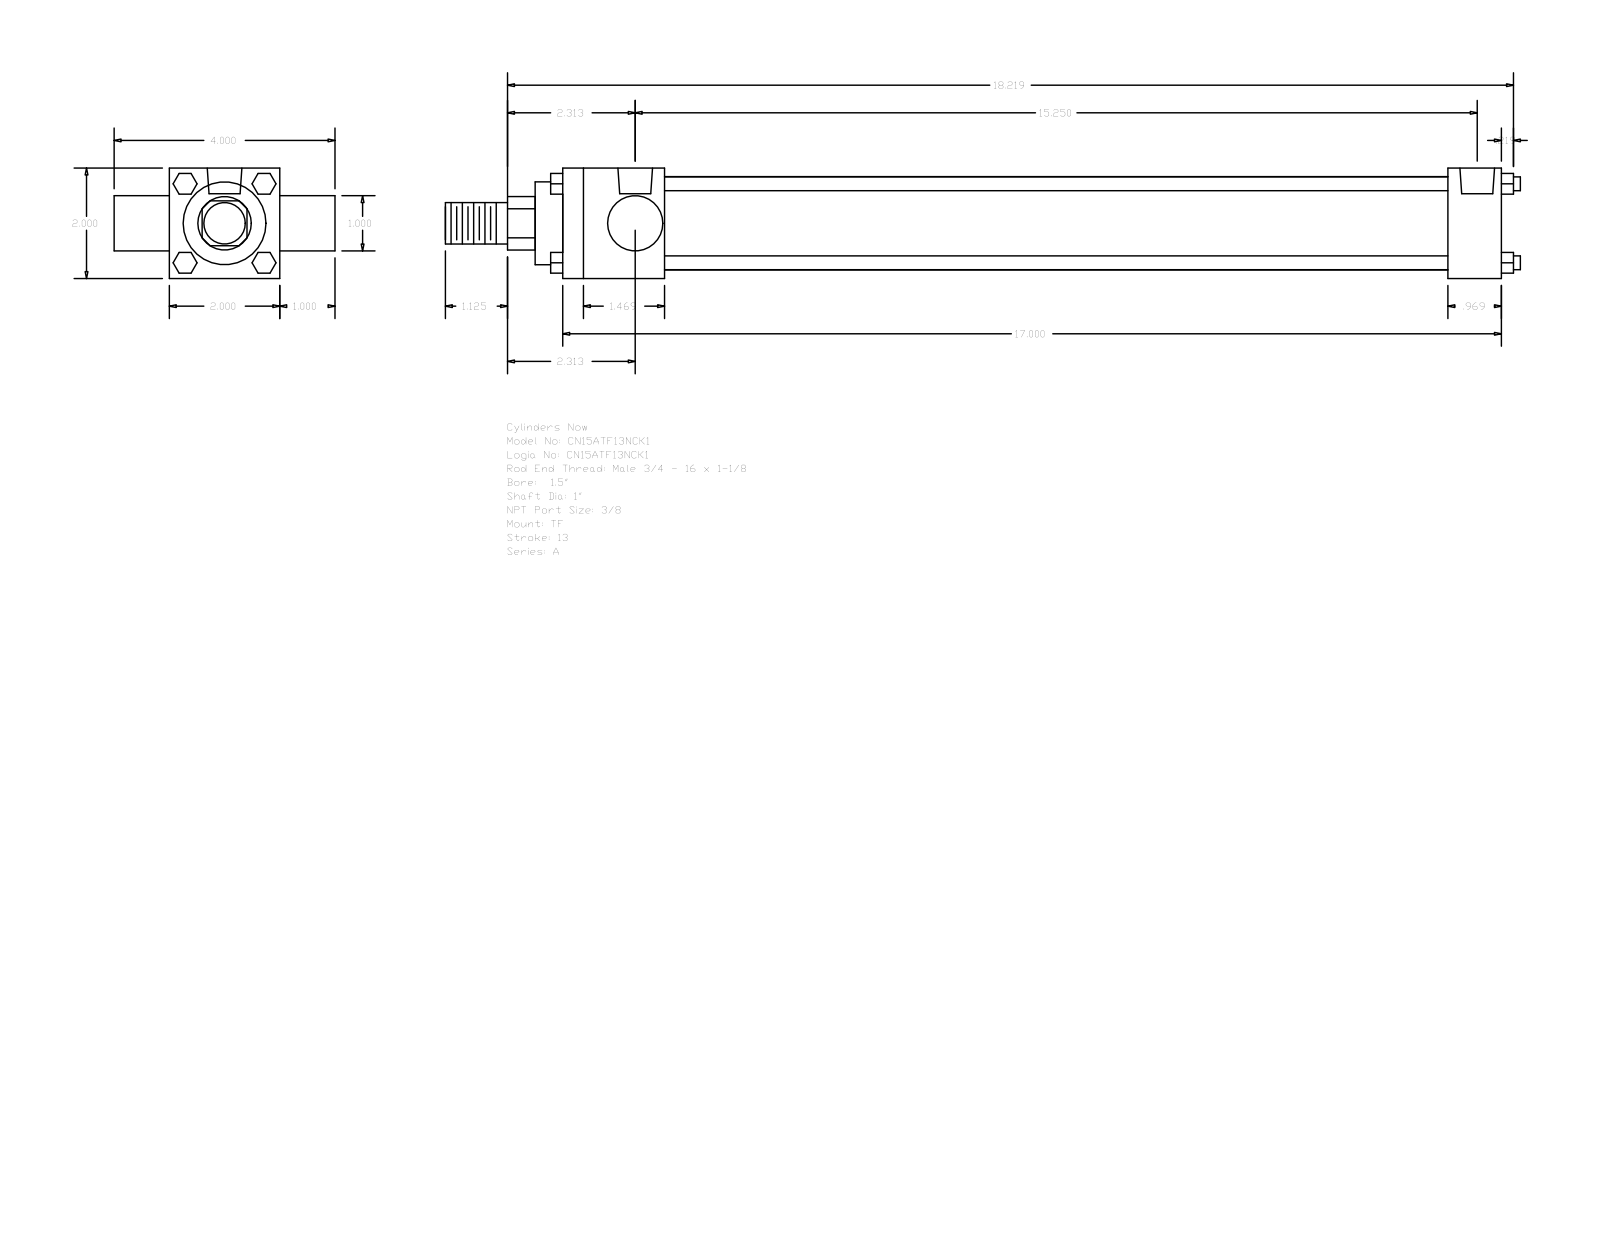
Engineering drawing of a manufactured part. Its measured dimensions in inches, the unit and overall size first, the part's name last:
Units: inches
Overall size (bounding box): 19.469 × 4 × 2
Round holes (diameter × count): ⌀0.219 ×3, ⌀0.627 ×2
Round bosses / shafts (diameter × count): ⌀0.25 ×4, ⌀1 ×2, ⌀1.69 ×1, ⌀1.5 ×1, ⌀0.75 ×1
Partial cylindrical surfaces — rounded edges, fillets, slot ends (radius × count): R0.484 ×1
Main face-to-face distances: 2, 1, 17, 3, 1.844, 16.031, 14.187, 15.156, 0.969, 0.5
Hole centre spacings: 0.156, 15.094, 14.937, 15.25
Bodies: 0 solids, 120 faces (92 planar, 28 cylindrical, 0 other)
Part name (STEP PRODUCT): A_TF__0150_1
STEP written by: GSSL Pune (CONFIG_CONTROL_DESIGN)
